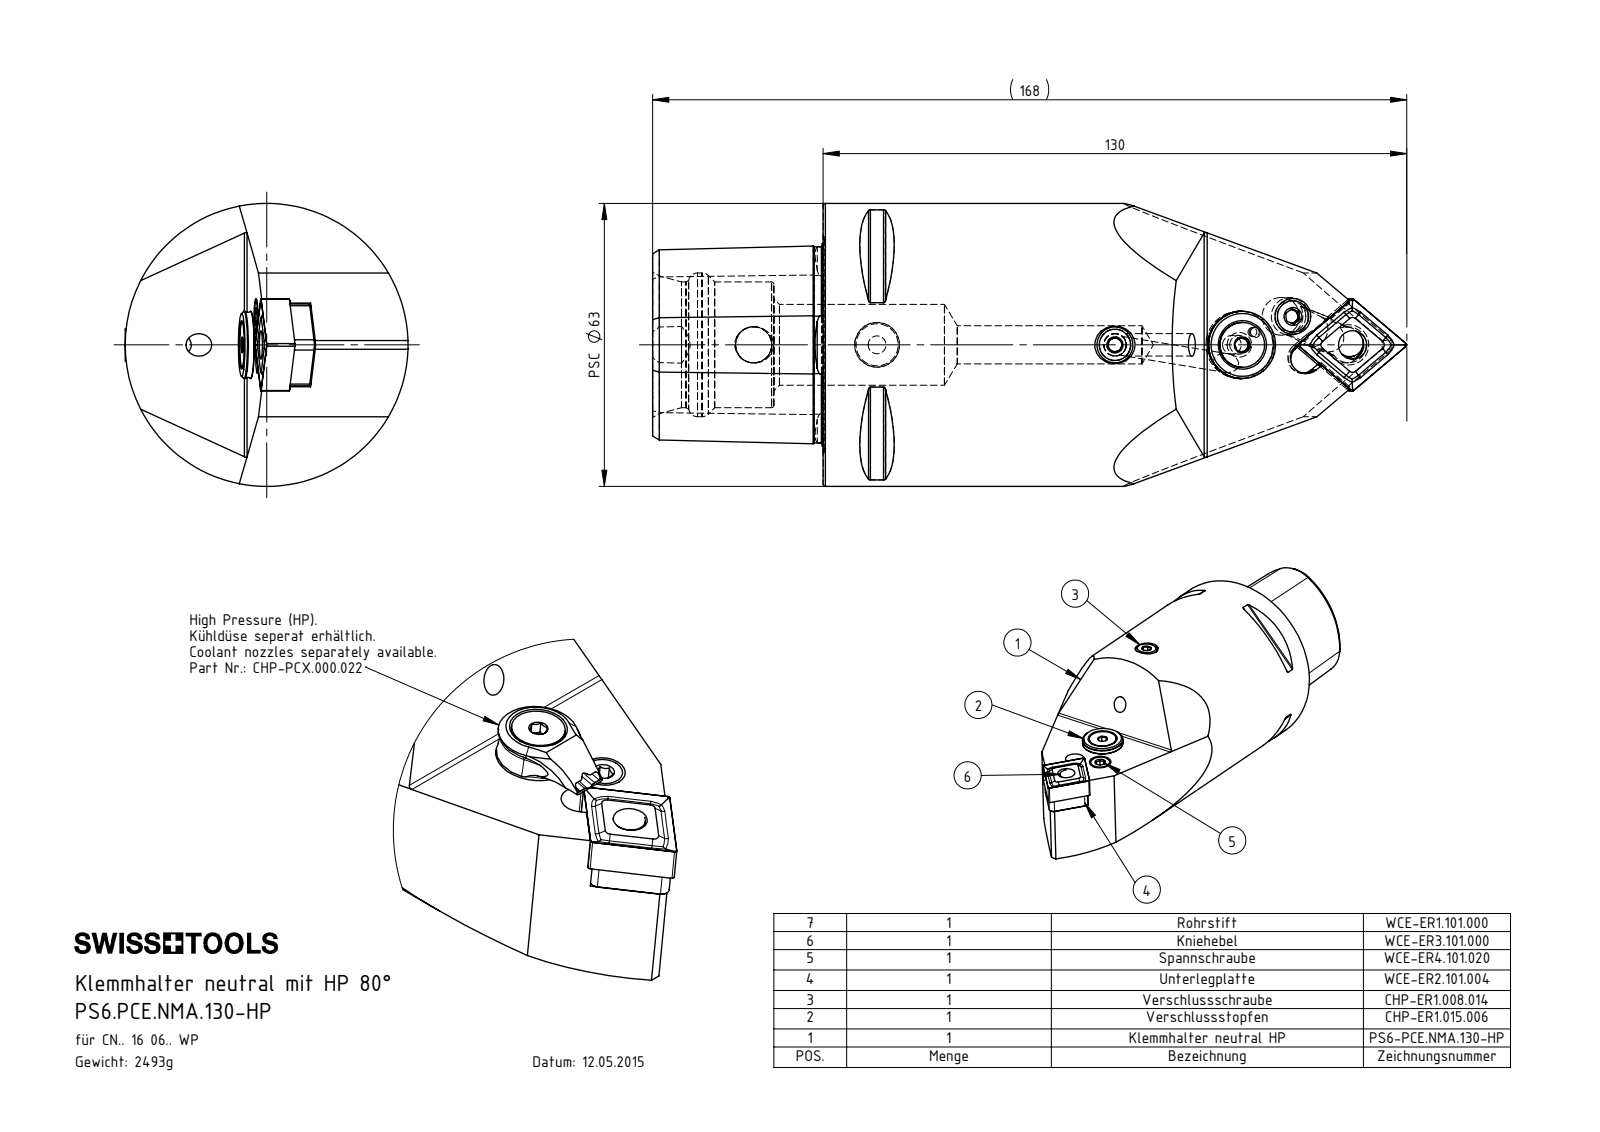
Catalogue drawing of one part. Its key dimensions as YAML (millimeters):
part_name: "CHP-ER1.015.006; CHP-ER1.008.014_A; DIN 7991 - M5x15; CHP-ER1.015.006_A (+8 more)"
step_written_by: "SolidWorks 2017 (AUTOMOTIVE_DESIGN)"
units: millimeters
bodies: {solids: 11, faces: 446, planar: 134, cylindrical: 115, other: 197}
overall_size: [168, 63, 63]
volume: 330868
surface_area: 46241
round_holes:
  - {diameter: 4.2, count: 3}
  - {diameter: 7, count: 2}
  - {diameter: 1.2, count: 1}
  - {diameter: 2, count: 1}
  - {diameter: 2.5, count: 1}
  - {diameter: 3, count: 1}
  - {diameter: 4, count: 1}
  - {diameter: 5, count: 1}
  - {diameter: 5.2, count: 1}
  - {diameter: 6.35, count: 1}
  - {diameter: 8.05, count: 1}
  - {diameter: 8.1, count: 1}
round_bosses_or_shafts:
  - {diameter: 8, count: 2}
  - {diameter: 63, count: 1}
  - {diameter: 15, count: 1}
  - {diameter: 13.4, count: 1}
  - {diameter: 10, count: 1}
  - {diameter: 7.9, count: 1}
  - {diameter: 6.4, count: 1}
  - {diameter: 6, count: 1}
partial_cylinders:
  - {radius: 0.5, count: 10}
  - {radius: 0.4, count: 4}
  - {radius: 1.5, count: 4}
  - {radius: 3.5, count: 4}
  - {radius: 0.3, count: 2}
  - {radius: 3.1, count: 1}
  - {radius: 3.6, count: 1}
  - {radius: 3.75, count: 1}
face_to_face_distances: [38, 15.12, 24.88, 10.81, 6.3, 4.51, 27, 11, 29.71, 4.76]
hole_center_spacings: [16.2, 4.5, 4.51, 4.52, 4.53, 14.75, 14.99, 16.01]
